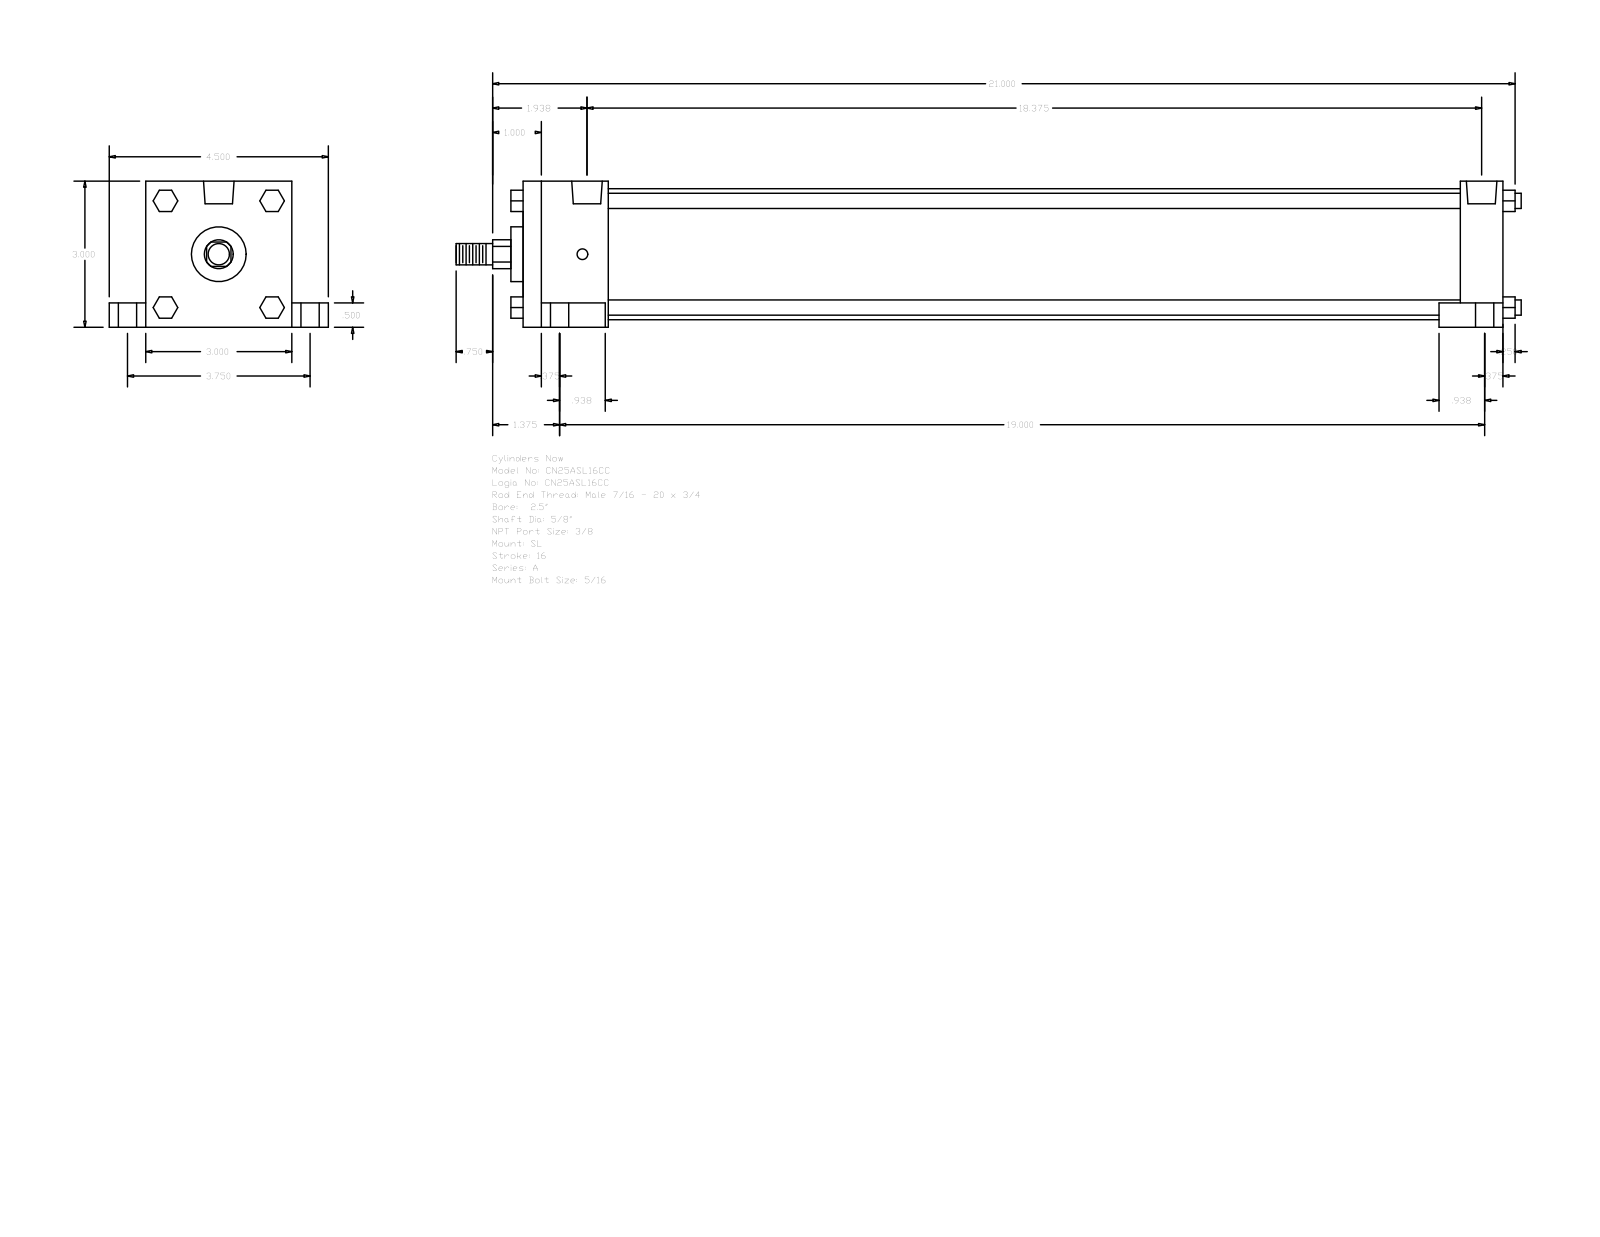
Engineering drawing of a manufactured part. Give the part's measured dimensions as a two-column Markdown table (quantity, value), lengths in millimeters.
| quantity | value |
| --- | --- |
| part name | A_SL__0250_0.625 |
| STEP written by | GSSL Pune (CONFIG_CONTROL_DESIGN) |
| units | millimeters |
| bodies | 0 solids, 148 faces (112 planar, 36 cylindrical, 0 other) |
| overall size | 555.62 × 114.3 × 76.2 |
| round holes (diameter × count) | 5.56 × 4, 9.53 × 4, 15.88 × 4, 15.93 × 2 |
| round bosses / shafts (diameter × count) | 7.94 × 4, 68.33 × 1, 28.57 × 1, 15.88 × 1, 11.11 × 1 |
| partial cylindrical surfaces (radius × count) | 7.54 × 1 |
| main face-to-face distances | 76.2, 511.17, 44.45, 466.72, 488.94, 444.49, 22.23, 63.5, 12.7, 19.05 |
| hole center spacings | 2.38, 47.63, 47.65, 49.09, 49.72, 95.24, 469.11, 470.72 |
